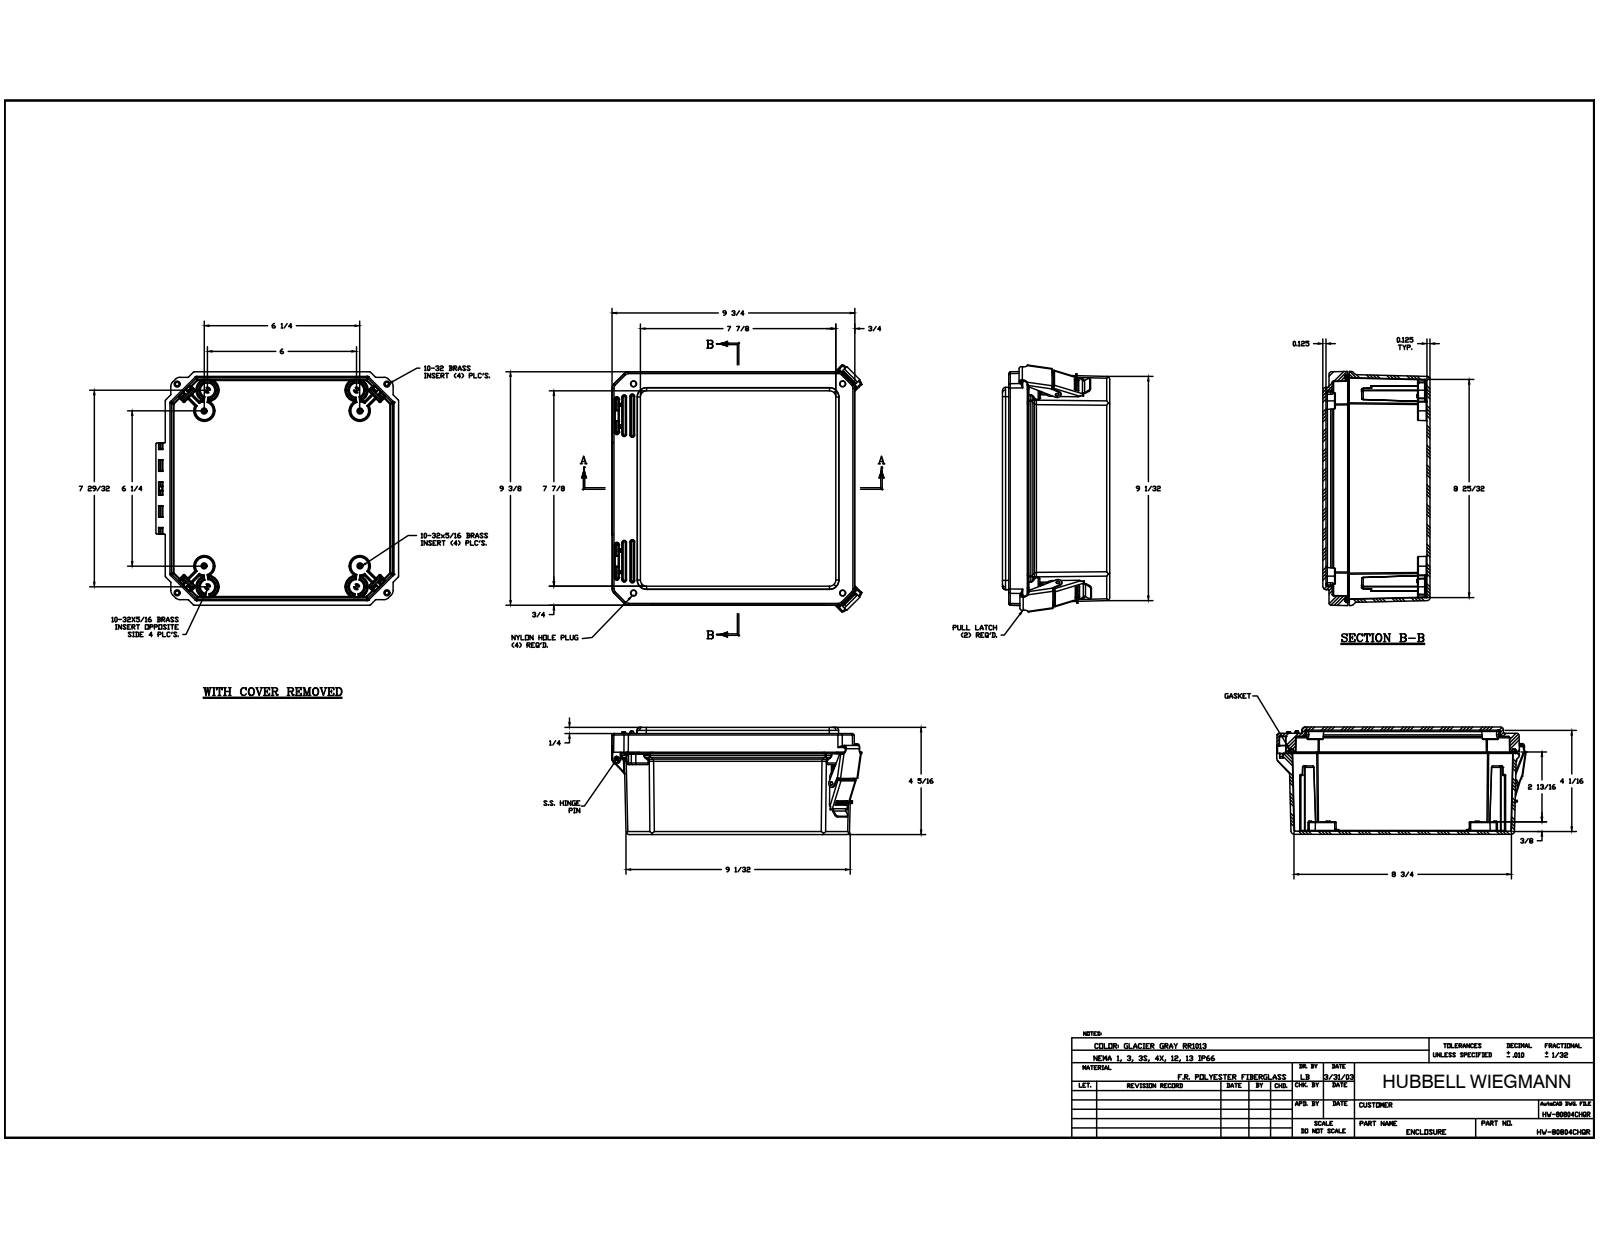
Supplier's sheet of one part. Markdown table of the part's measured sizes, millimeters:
| quantity | value |
| --- | --- |
| part name | DS080804BOX; BRASS INSERT-(; BRASS INSERT-(_1; BRASS INSERT-(_2 (+6 more) |
| STEP written by | Autodesk Inventor 2014 (AUTOMOTIVE_DESIGN) |
| units | millimeters |
| bodies | 35 solids, 2376 faces (809 planar, 951 cylindrical, 616 other) |
| overall size | 256.41 × 255.16 × 109.48 |
| volume | 859 259 mm³ |
| surface area | 479 825 mm² |
| round holes (diameter × count) | 3.96 × 16, 3.43 × 9, 3.86 × 8, 3.81 × 4, 6.4 × 4, 6.43 × 4, 3.43 × 2, 5.56 × 2, 5.77 × 2, 7.94 × 2, 9.52 × 2, 3.48 × 1 |
| round bosses / shafts (diameter × count) | 6.25 × 16, 22.1 × 4, 7.62 × 4, 5.3 × 4, 3.43 × 3, 11.05 × 2 |
| partial cylindrical surfaces (radius × count) | 0.25 × 155, 0.51 × 92, 0.13 × 80, 0.76 × 62, 1.52 × 33, 1.59 × 28, 2.29 × 26, 0.76 × 24 |
| main face-to-face distances | 3.17, 106.31, 109.48, 103.14, 3.15, 6.35, 99.96, 3.18, 9.53, 103.13 |
| hole center spacings | 169.24, 6.35, 158.75, 158.76, 187.93, 238.9, 21.27, 156.99 |
